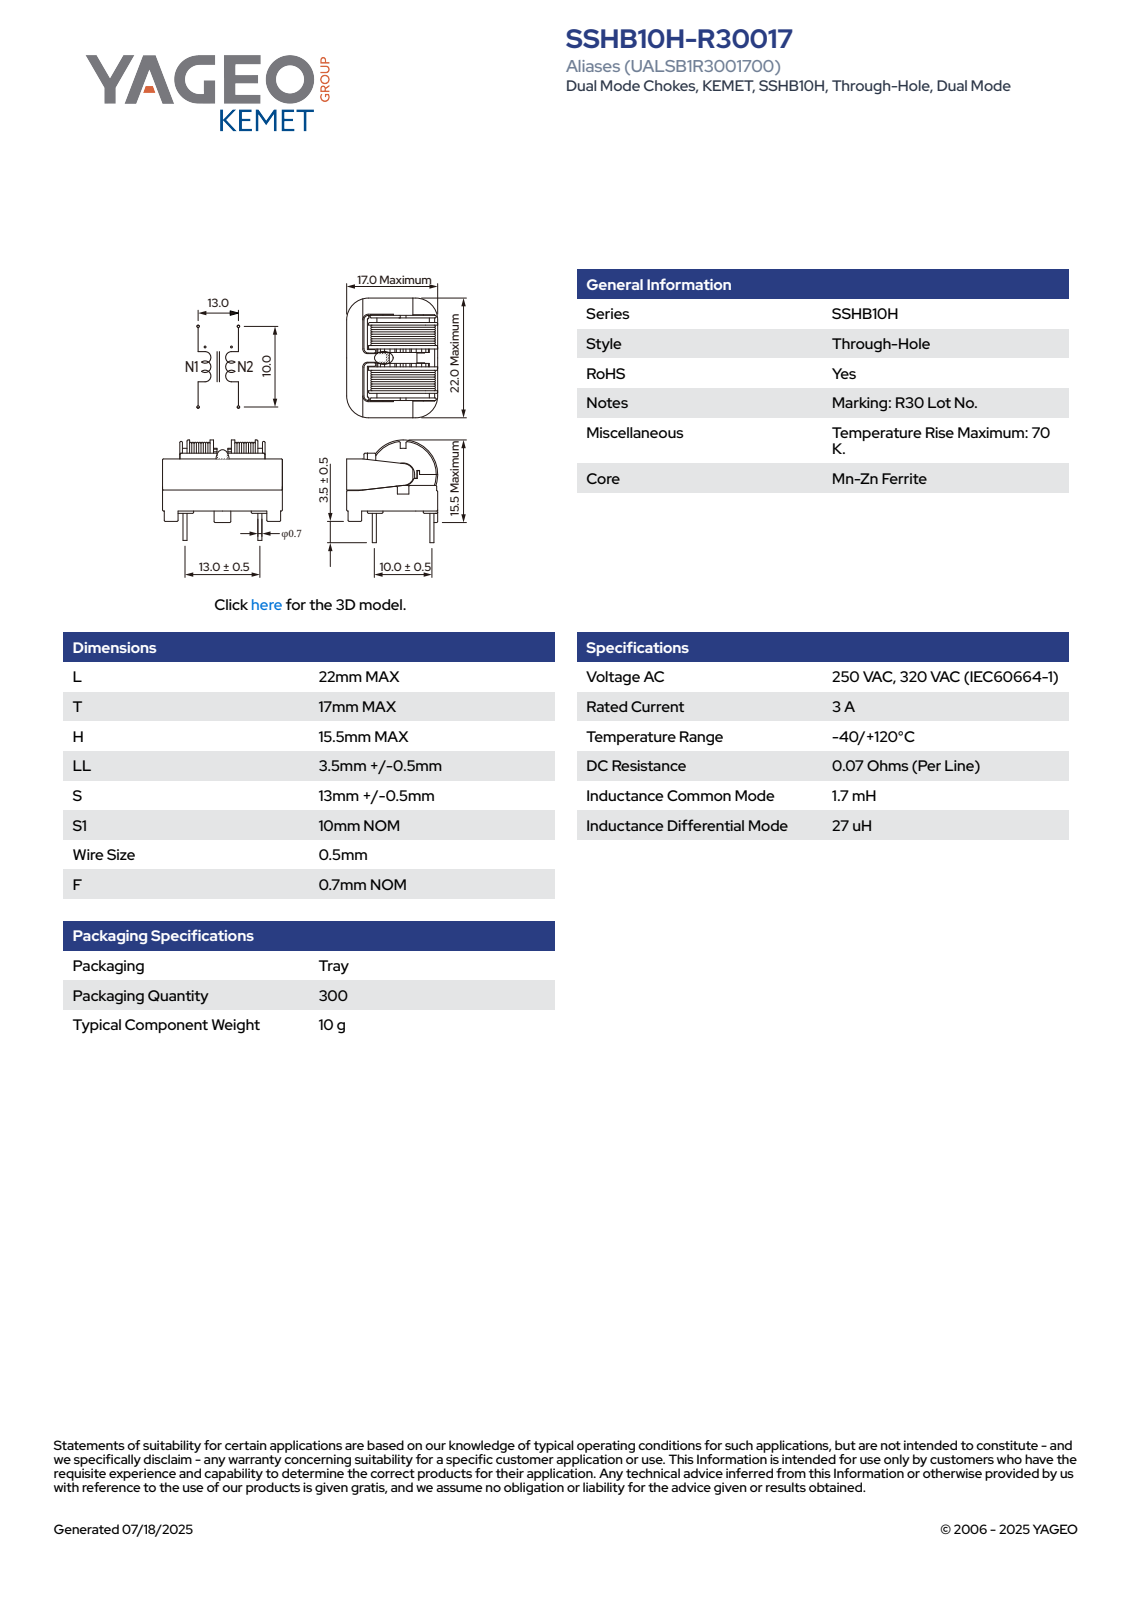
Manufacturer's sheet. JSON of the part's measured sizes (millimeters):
{"part_name": "SSHB10H(MAX-LOGO)", "step_written_by": "SolidWorks 2018 (AUTOMOTIVE_DESIGN)", "units": "millimeters", "bodies": {"solids": 1, "faces": 397, "planar": 273, "cylindrical": 92, "other": 32}, "overall_size": [22, 19.02, 17], "volume_mm3": 3002, "surface_area_mm2": 3354, "round_holes": [[4.1, 1]], "round_bosses_or_shafts": [[0.7, 4], [12, 1], [11.5, 1], [9.1, 1], [6.3, 1], [3.8, 1]], "partial_cylinders_radius": [[0.2, 26], [0.8, 6], [3.8, 4], [1, 2], [5, 2], [5, 2], [1.8, 1], [4.75, 1]], "face_to_face_distances": [0.6, 8.95, 3.6, 18.4, 2.39, 8.4, 4.05, 9.46, 12.54, 5.86]}
